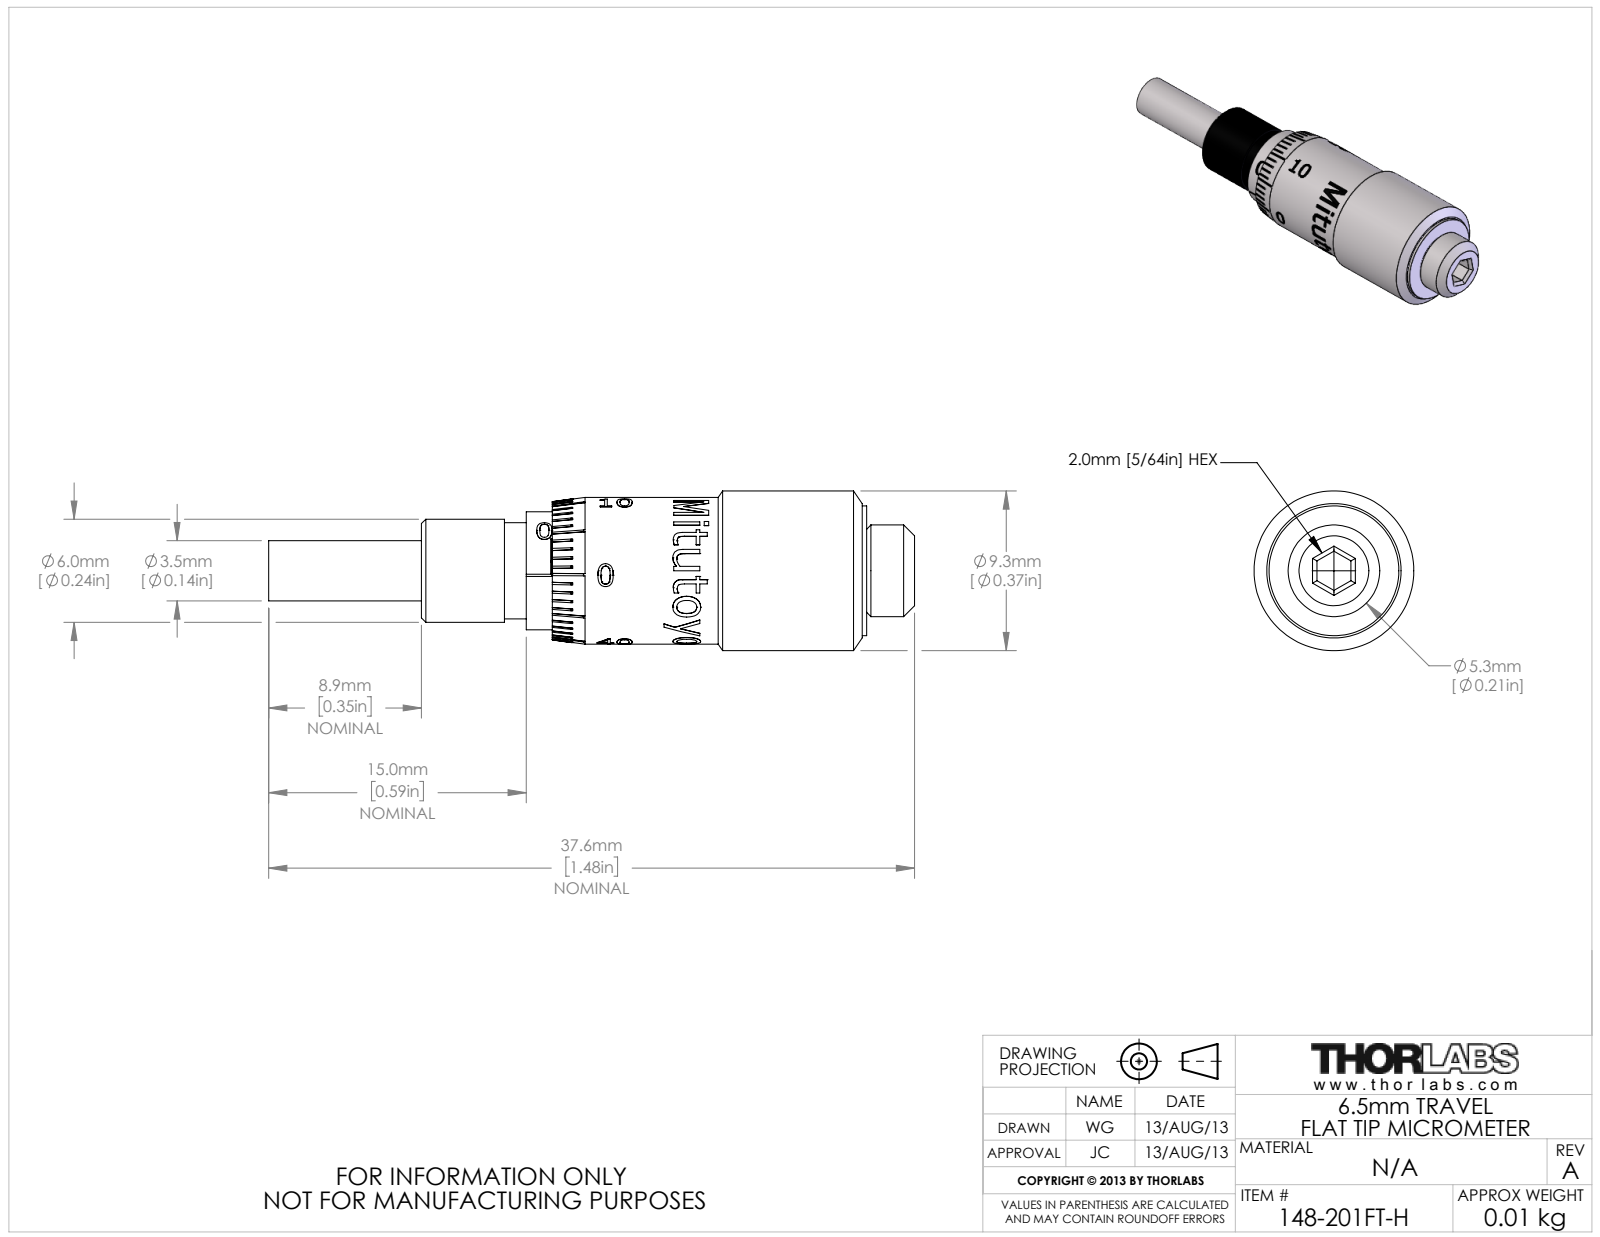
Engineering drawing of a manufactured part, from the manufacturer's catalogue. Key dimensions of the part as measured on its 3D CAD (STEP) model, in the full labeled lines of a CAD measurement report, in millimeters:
Part name (STEP PRODUCT): TTN017216-E0W
STEP written by: SolidWorks 2012 (AUTOMOTIVE_DESIGN)
Units: millimetres
Bodies: 2 solids, 533 faces (226 planar, 91 cylindrical, 216 other)
Overall size (bounding box): 37.6 × 9.3 × 9.3
Volume: 1 500 mm³ · Surface area: 1 051 mm²
Round holes (diameter × count): ⌀2.3 ×1
Round bosses / shafts (diameter × count): ⌀9.3 ×1, ⌀8.5 ×1, ⌀7.5 ×1, ⌀6.9 ×1, ⌀6 ×1, ⌀5.6 ×1, ⌀5.3 ×1, ⌀3.5 ×1
Partial cylindrical surfaces — rounded edges, fillets, slot ends (radius × count): R3.4 ×1, R4.2 ×1, R4.3 ×1, R4.3 ×1
Main face-to-face distances: 25.9, 7.6, 18.3, 6.1, 1.5, 19.8, 2.8, 21.1, 8.9, 15
